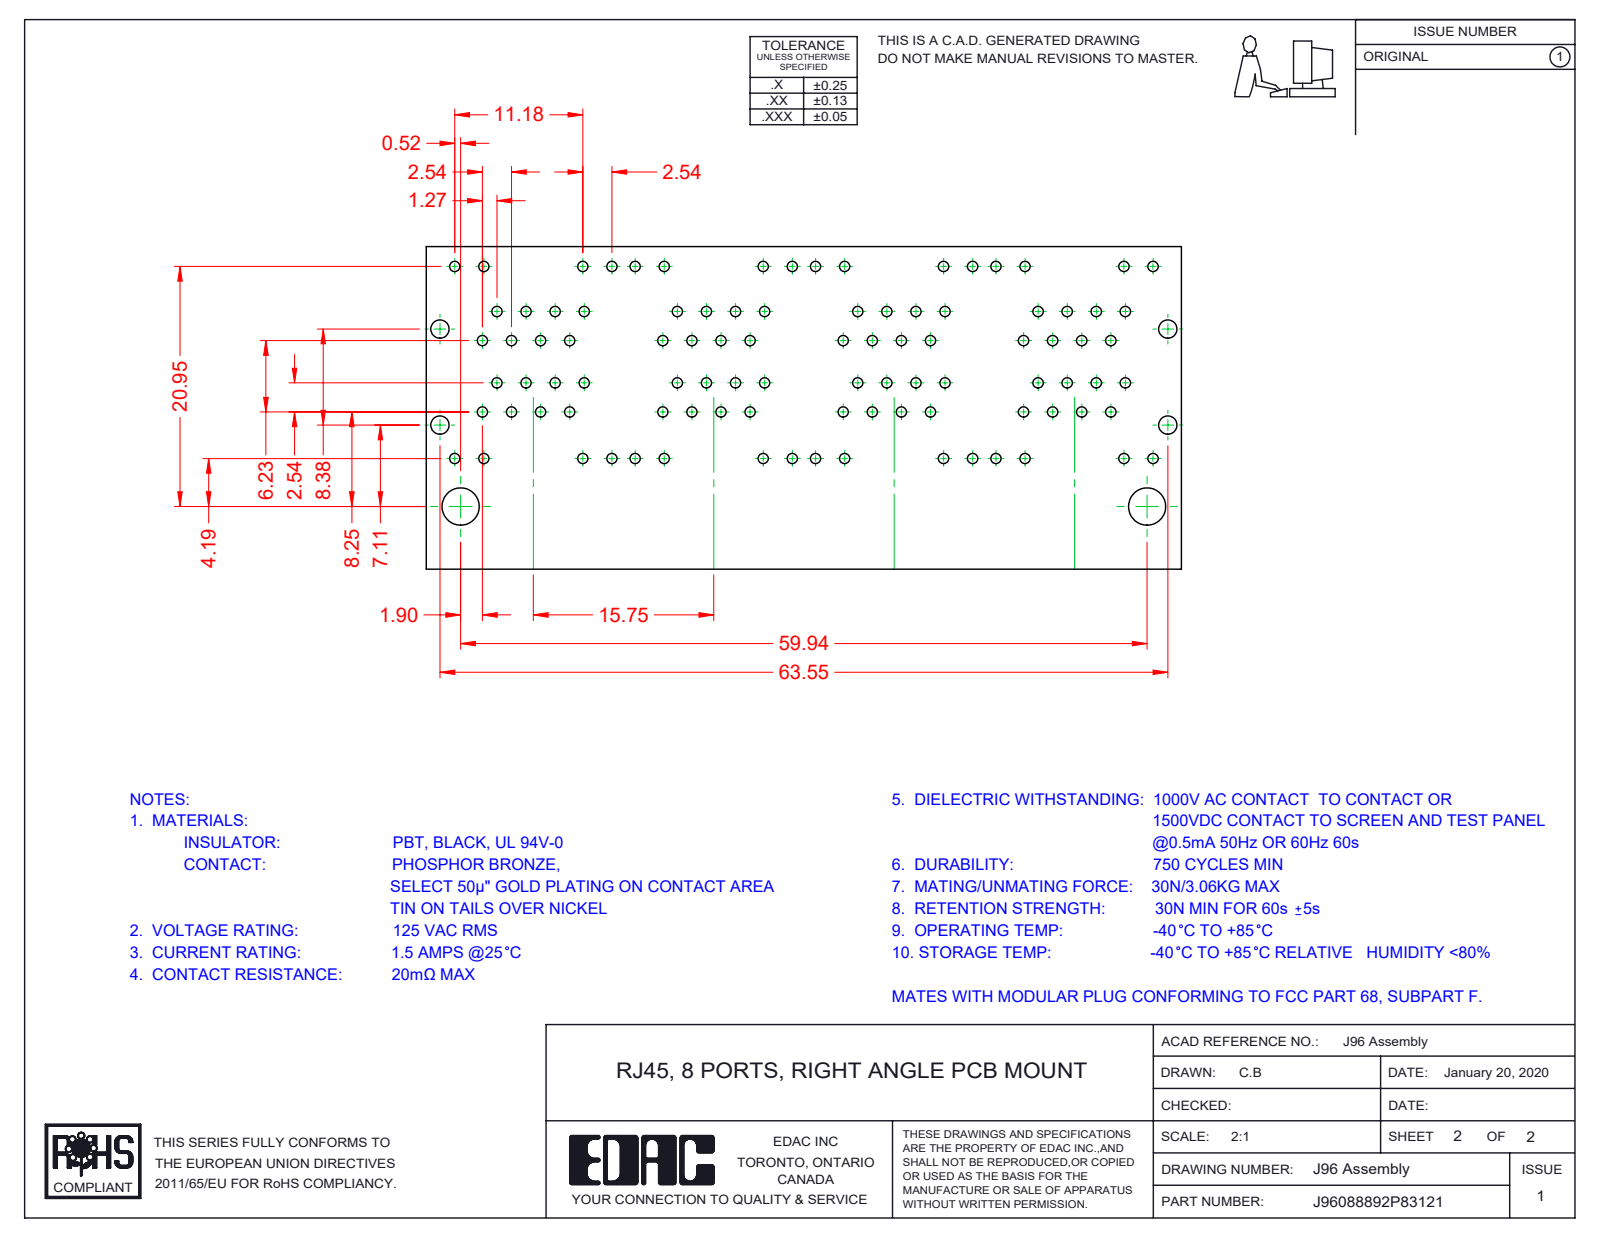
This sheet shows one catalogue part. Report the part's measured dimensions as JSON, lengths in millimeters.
{"part_name": "96 LED RH Lower_3-Green; 96 Grounding_8 Ports; 96 LED LH Lower_8-Red-Yellow; 96 Contact Lock Lower (+8 more)", "step_written_by": "SolidWorks 2016 (CONFIG_CONTROL_DESIGN)", "units": "millimeters", "bodies": {"solids": 96, "faces": 7658, "planar": 6069, "cylindrical": 1323, "other": 266}, "overall_size": [64.05, 29.58, 28.68], "volume_mm3": 24160, "surface_area_mm2": 63658, "round_holes": [[1.7, 3]], "round_bosses_or_shafts": [[1.68, 3]], "partial_cylinders_radius": [[0.25, 124], [0.35, 73], [1, 72], [0.5, 49], [0.91, 32], [0.2, 21], [0.7, 11], [0.22, 8]], "face_to_face_distances": [15.75, 0.35, 9.95, 1.17, 1.6, 0.54, 9.98, 10.18, 12.67, 3.37], "hole_center_spacings": [15.75, 31.5]}
